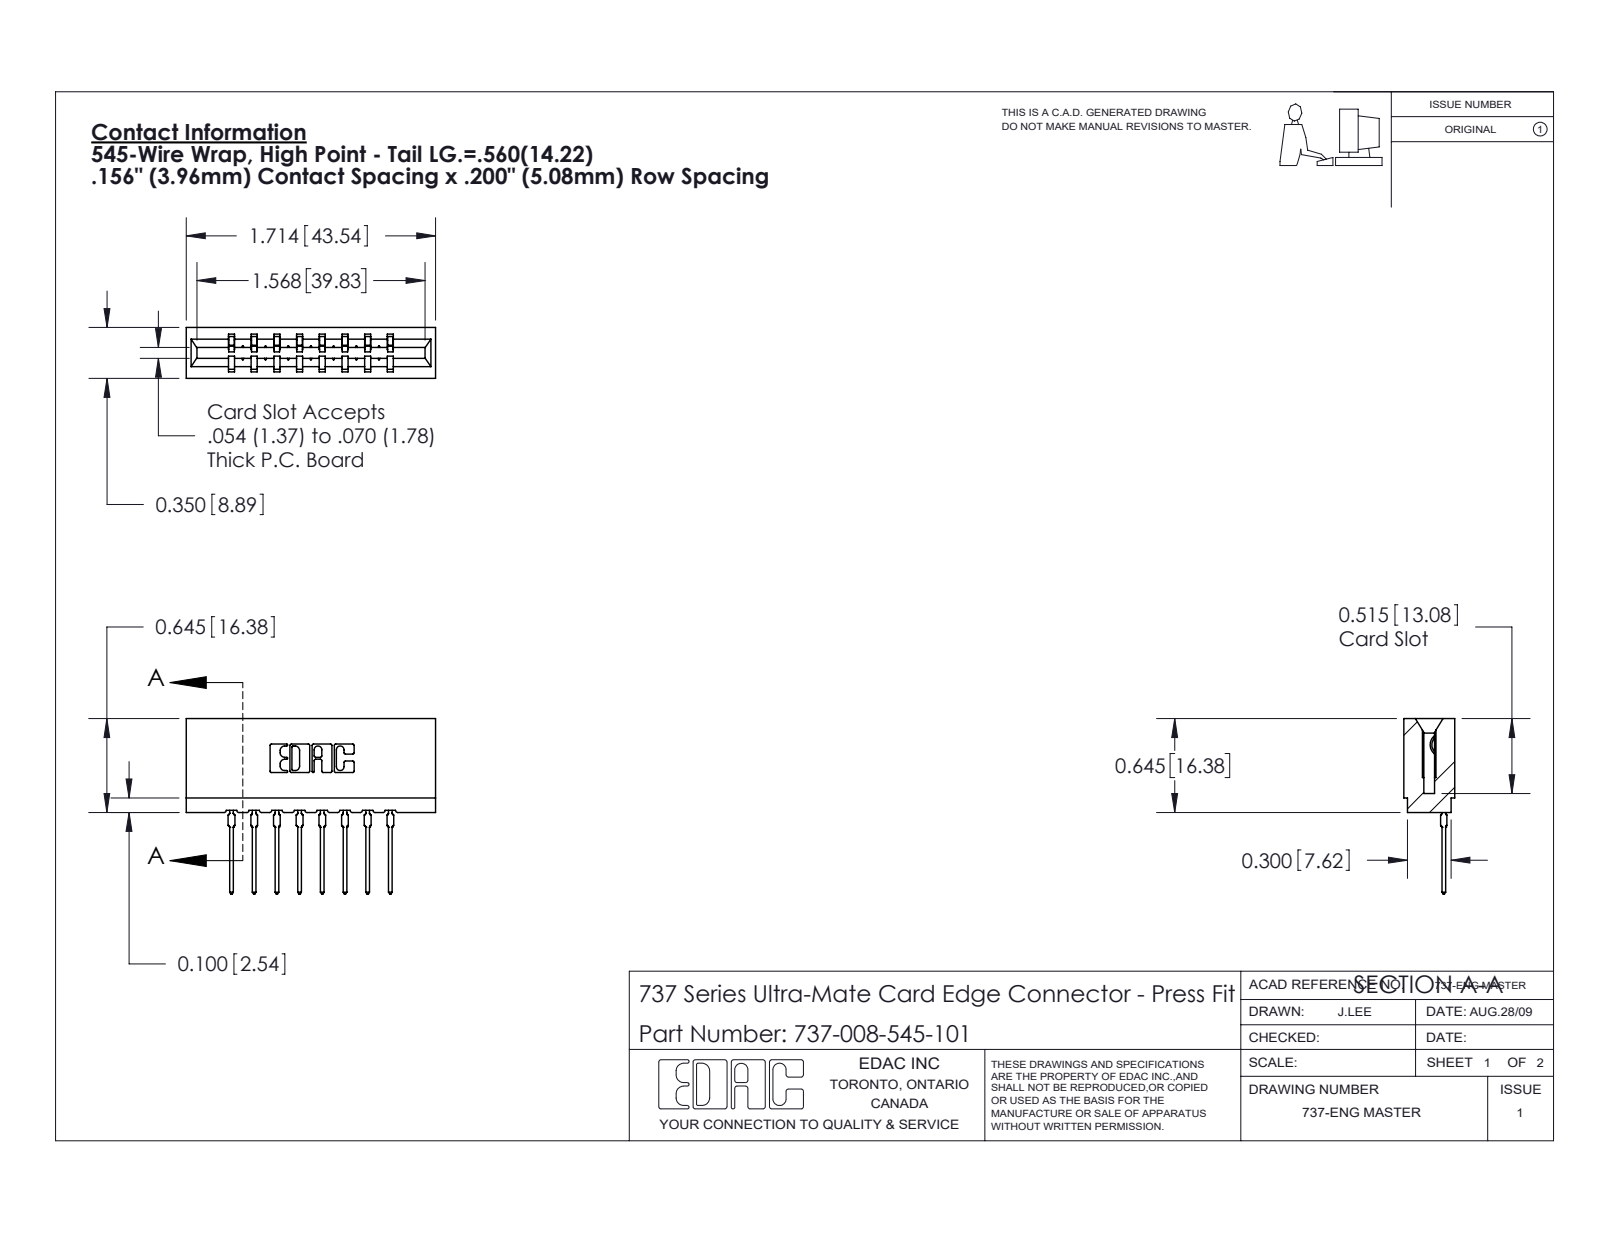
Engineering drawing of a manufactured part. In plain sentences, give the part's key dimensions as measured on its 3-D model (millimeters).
The part is named "737-008-545-101; 745-292-001_545; 737 Part_Insulator Option - 01". Its 3-D file was written by "SolidWorks 2020 (CONFIG_CONTROL_DESIGN)". It is 9 solids with 998 faces: 598 planar, 192 cylindrical and 208 other. Overall it measures 43.5 by 30.6 by 8.9 millimeters. Its volume is 4 470 cubic millimeters and its surface area 5 503 square millimeters. Partial cylindrical surfaces (rounded edges, fillets, slot ends): 22 of radius 0.3, 16 of radius 0.4, 16 of radius 0.5, 6 of radius 0.2, 6 of radius 0.8, 4 of radius 0.1, 4 of radius 0.3, 3 of radius 0.7. The main face-to-face distances are 4, 3.5, 5.4, 8.9, 15.8, 7.9, 9, 5, 11.9, 19.8.
